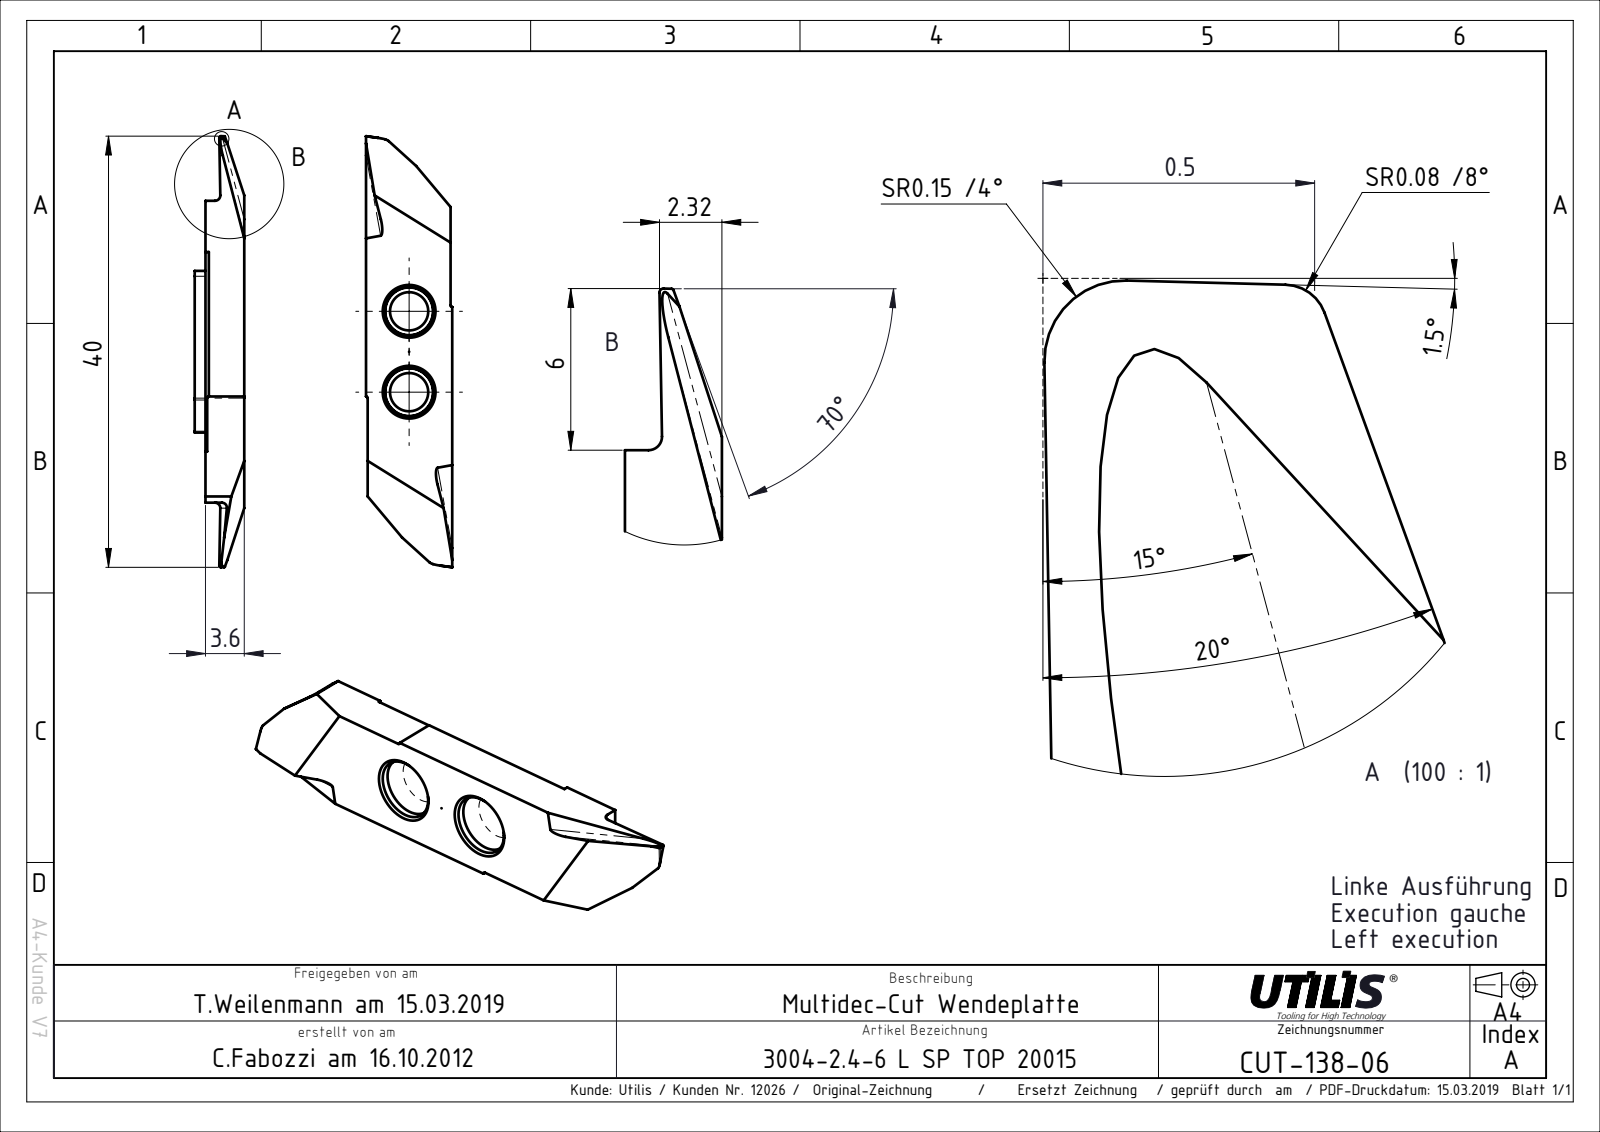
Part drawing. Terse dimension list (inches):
name: CUT-138-06
written by: SolidWorks 2022 (AUTOMOTIVE_DESIGN)
unit: in
bodies: 1 solid, 67 faces (33 planar, 22 cylindrical, 12 other)
size: 1.575 × 0.315 × 0.181
volume: 0.052 in³; area: 1.42 in²
holes: 2× ⌀0.14
rounds: 4× R0.006, 4× R0.012, 4× R0.02
face distances: 0.142, 0.315, 0.039, 0.181, 0.309, 0.303, 0.309, 0.256, 0.059, 0.912
hole spacings: 0.148, 0.295
